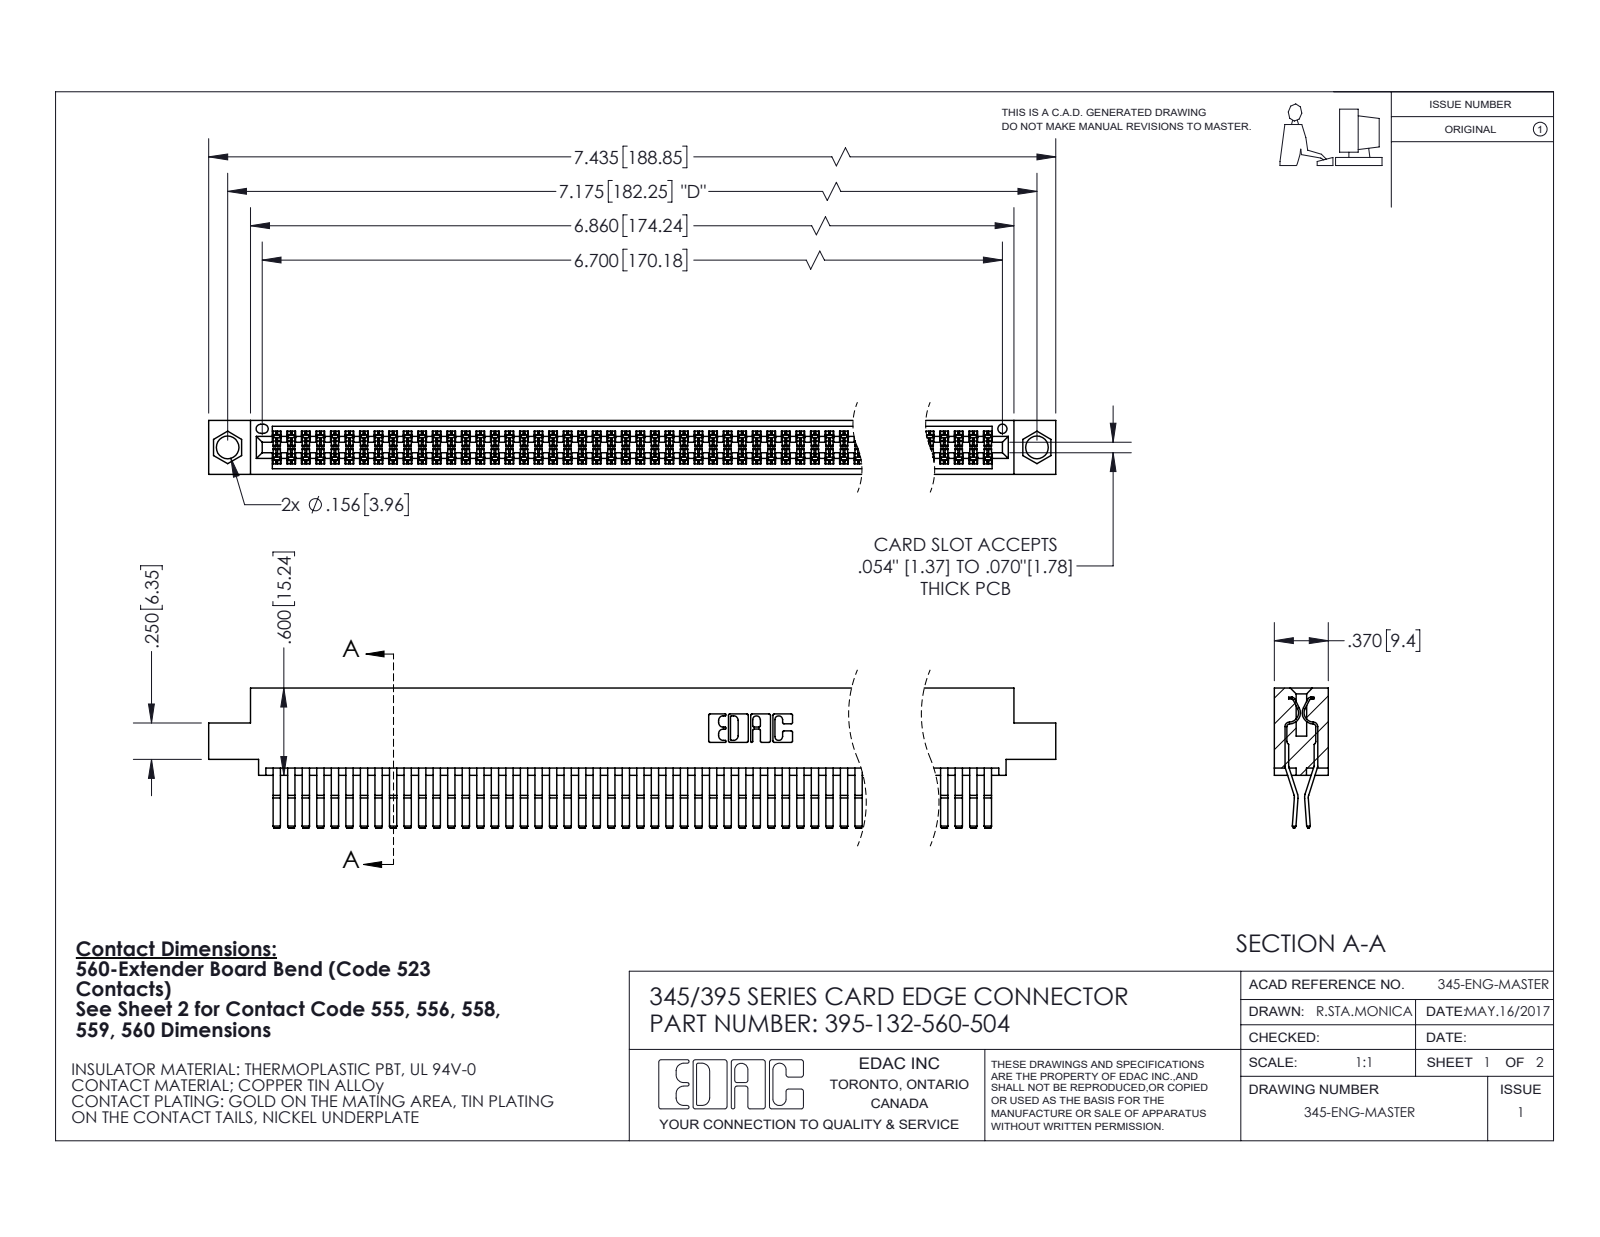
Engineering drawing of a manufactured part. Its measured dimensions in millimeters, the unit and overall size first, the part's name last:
Units: millimetres
Overall size (bounding box): 188.8 × 24.4 × 9.4
Round holes (diameter × count): ⌀4 ×2, ⌀1.6 ×1
Partial cylindrical surfaces — rounded edges, fillets, slot ends (radius × count): R0.2 ×198, R0.3 ×22, R0.2 ×6, R0.8 ×6, R0.7 ×3, R0.3 ×2, R0.4 ×2, R0.5 ×2
Main face-to-face distances: 0.6, 7.6, 1.8, 9.4, 5.1, 2.5, 6.9, 5.7, 4.4, 3.8
Hole centre spacings: 6.9, 176.3, 182.2
Volume: 19 250 mm³ · Surface area: 31 100 mm²
Bodies: 133 solids, 7008 faces (4454 planar, 2554 cylindrical, 0 other)
Part name (STEP PRODUCT): 345-292-001_560 Tail; 395-132-560-504; 345 Part_0.110 Offset - 0.156 Dia-TI
STEP written by: SolidWorks 2020 (CONFIG_CONTROL_DESIGN)
